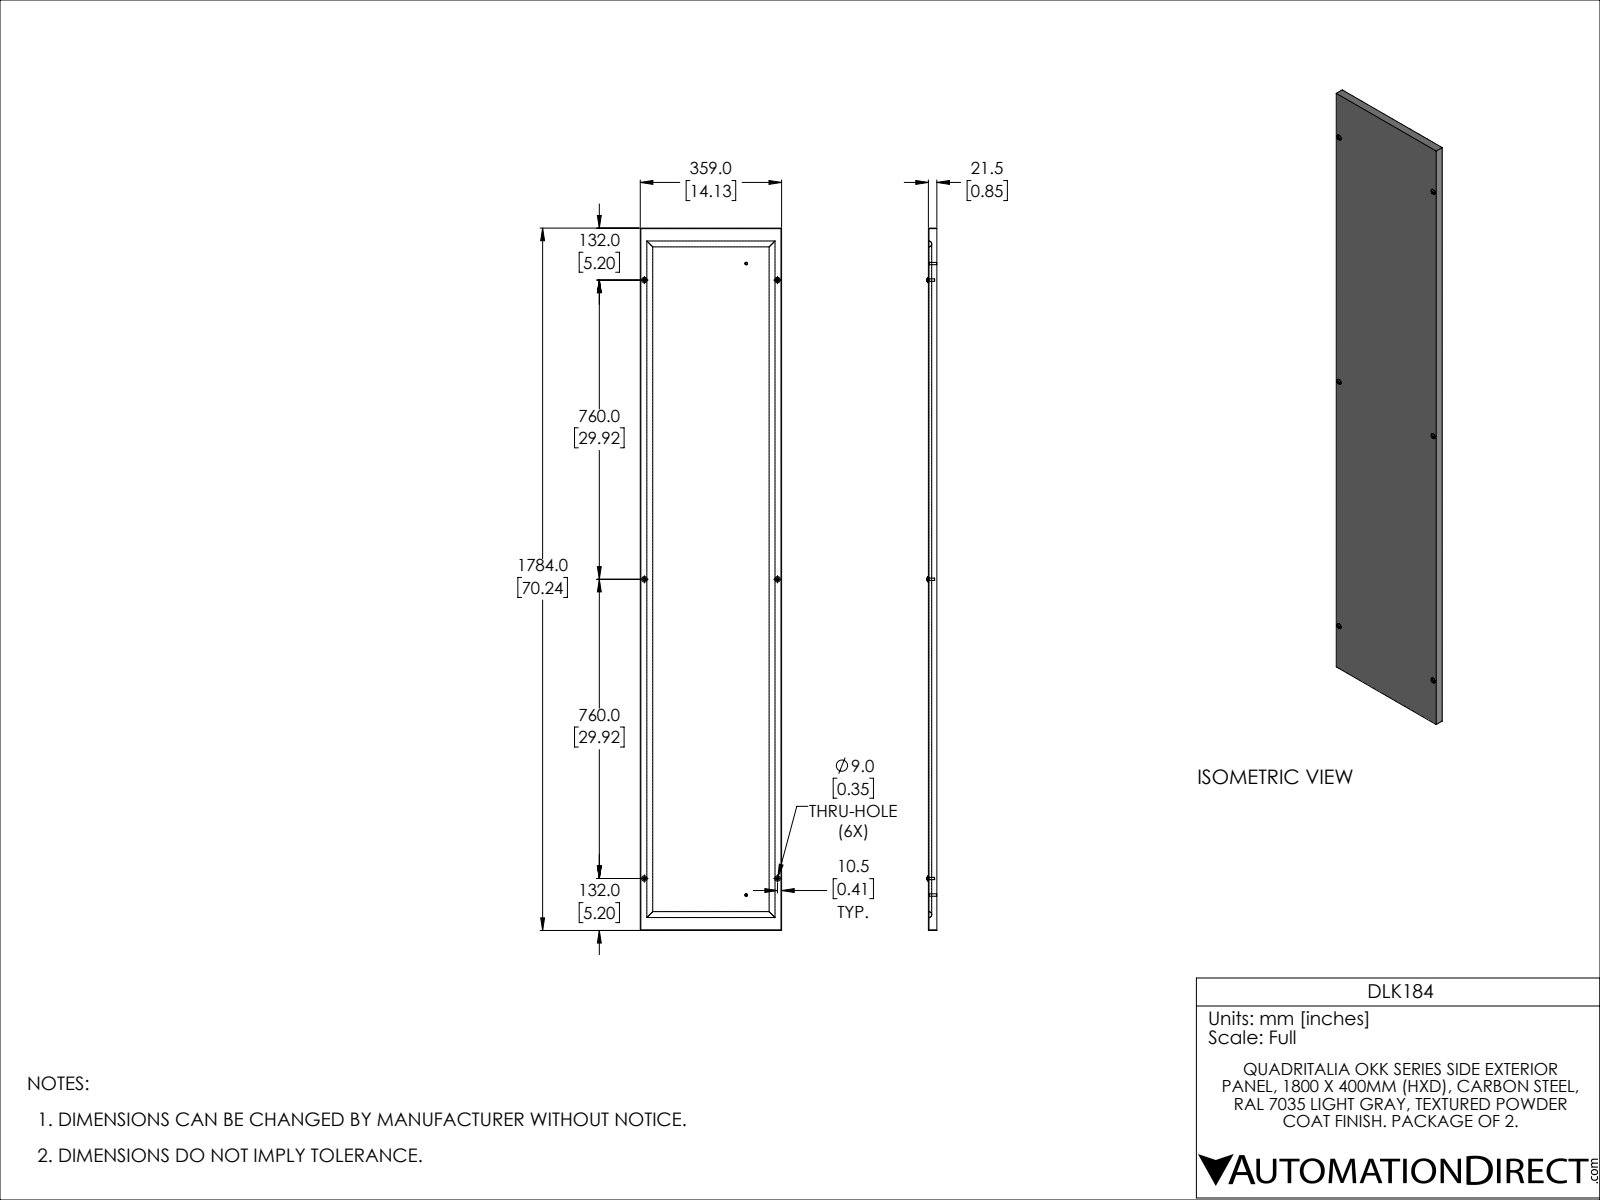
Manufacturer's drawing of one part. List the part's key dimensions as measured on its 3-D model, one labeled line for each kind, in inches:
Part name (STEP PRODUCT): DLK184
STEP written by: SolidWorks 2021 (CONFIG_CONTROL_DESIGN)
Units: inches
Bodies: 13 solids, 243 faces (125 planar, 98 cylindrical, 20 other)
Overall size (bounding box): 70.236 × 14.134 × 0.992
Volume: 86.69 in³ · Surface area: 2 504 in²
Round holes (diameter × count): ⌀0.354 ×6
Round bosses / shafts (diameter × count): ⌀0.236 ×8, ⌀0.551 ×6, ⌀0.276 ×2
Partial cylindrical surfaces — rounded edges, fillets, slot ends (radius × count): R0.02 ×72, R0.296 ×4
Main face-to-face distances: 0.059, 14.075, 14.134, 14.016, 70.177, 70.236, 70.118, 0.846, 0.787, 38.774
Hole centre spacings: 29.921, 32.747, 13.307, 59.843, 61.304
